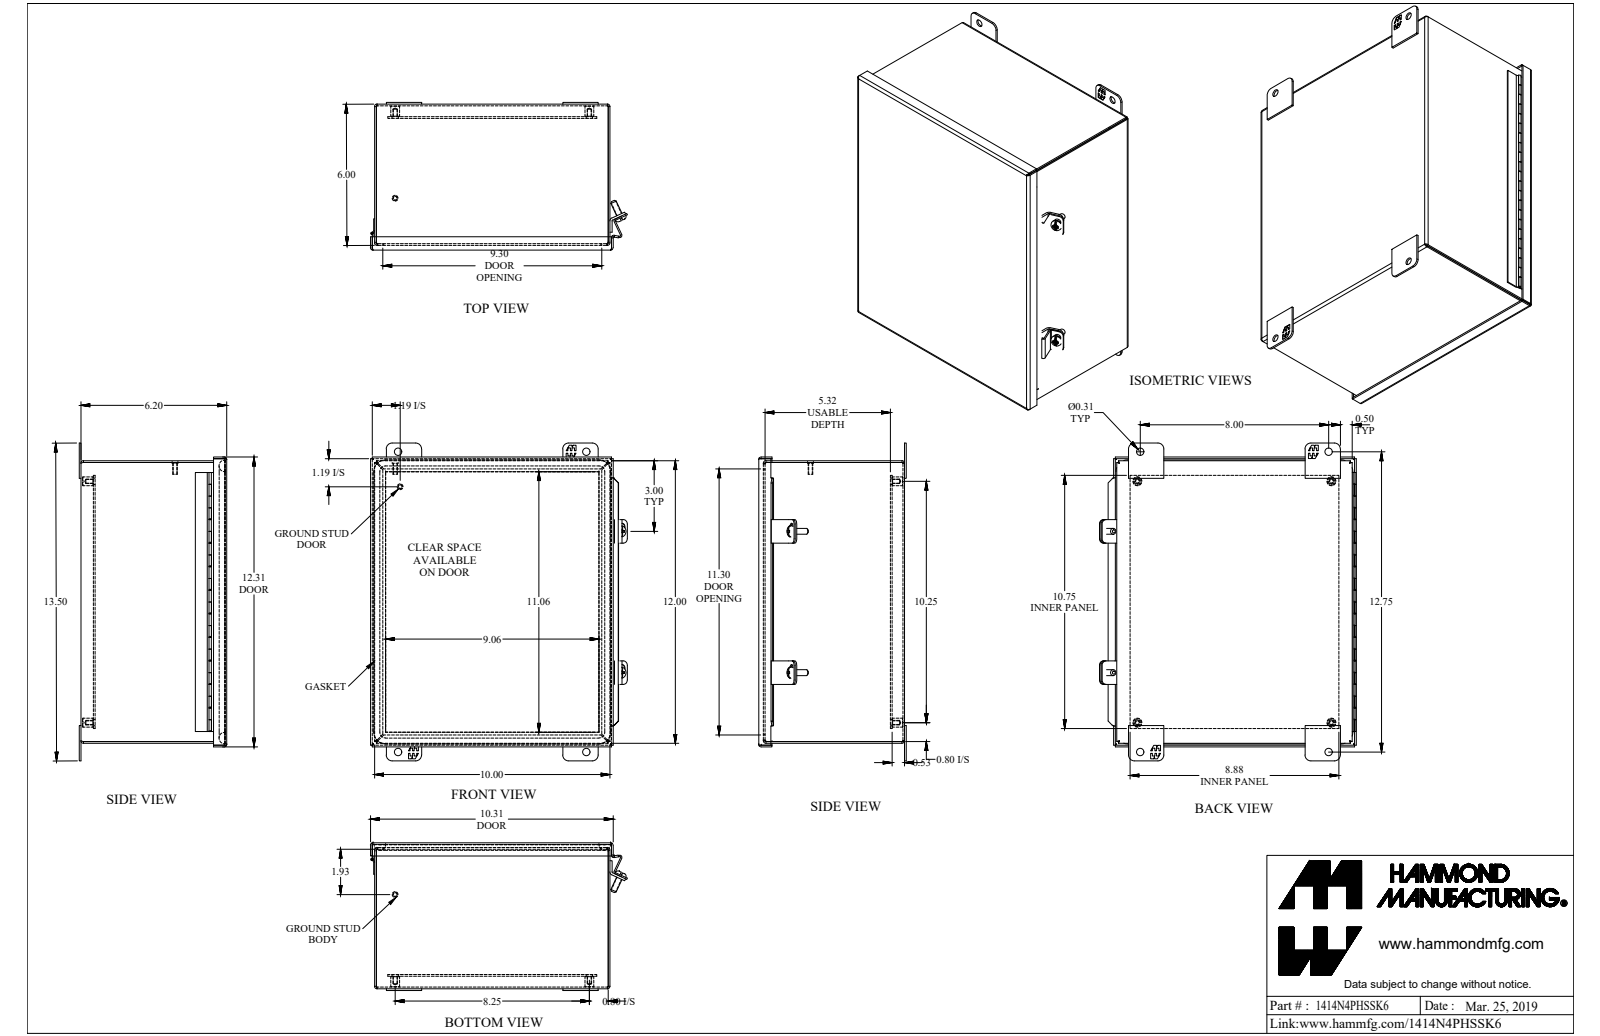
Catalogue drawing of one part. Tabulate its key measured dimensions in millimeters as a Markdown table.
| quantity | value |
| --- | --- |
| part name | 1414N4PHSSK6 |
| STEP written by | SolidWorks 2018 (AUTOMOTIVE_DESIGN) |
| units | millimeters |
| bodies | 21 solids, 724 faces (464 planar, 196 cylindrical, 64 other) |
| overall size | 342.9 × 276.9 × 159.2 |
| volume | 846 400 mm³ |
| surface area | 931 000 mm² |
| round holes (diameter × count) | 4 × 4, 6.7 × 4, 8 × 4, 5.4 × 2, 1.3 × 1 |
| round bosses / shafts (diameter × count) | 9.5 × 4, 6.4 × 4, 12.2 × 2, 4.8 × 2, 2.5 × 1, 1.1 × 1 |
| partial cylindrical surfaces (radius × count) | 6.4 × 24, 0.9 × 9, 2.7 × 9, 4.8 × 8, 0.1 × 4, 1.1 × 4, 2 × 4, 3 × 4 |
| main face-to-face distances | 1.8, 13.5, 1.9, 252.2, 155.6, 157.4, 155.5, 142.1, 153.7, 303 |
| hole center spacings | 357.7, 208.8, 334.2, 31.9, 31.9, 209.6, 209.6, 260.4 |
